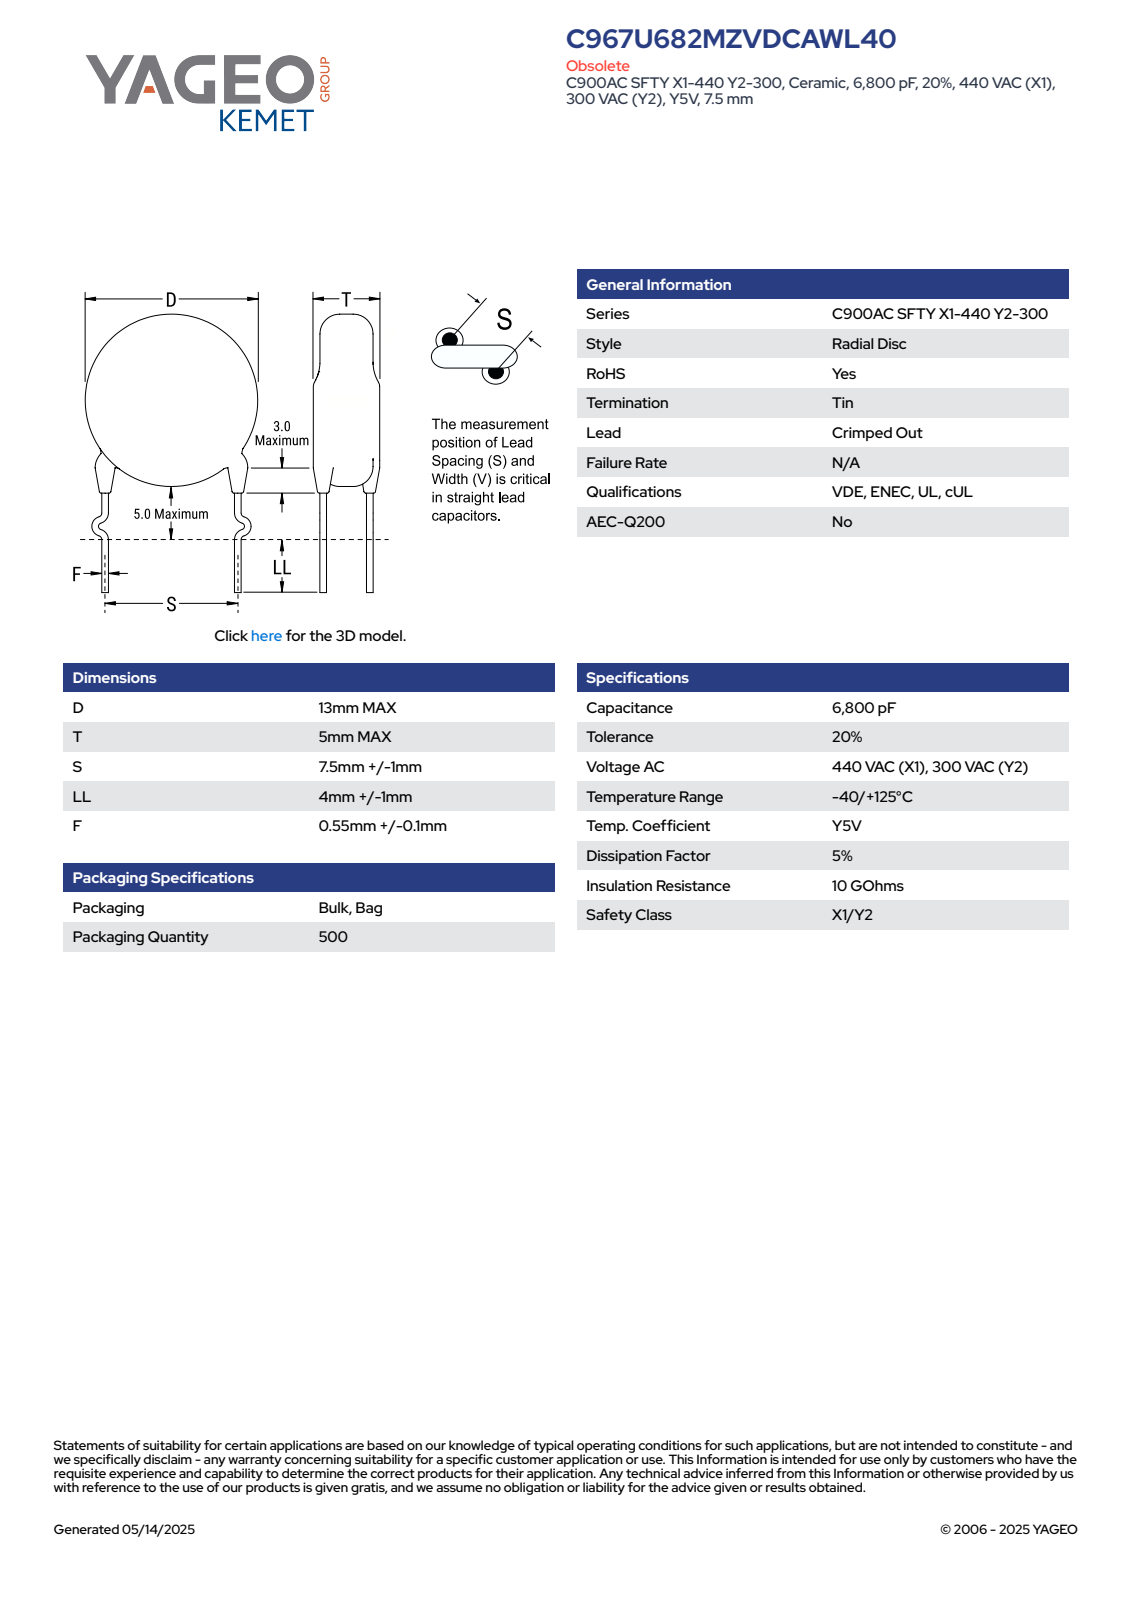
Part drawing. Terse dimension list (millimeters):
name: CCD_KCOC900_D13T5S7.5LL5F0.55
written by: SolidWorks 2014 (AUTOMOTIVE_DESIGN)
unit: mm
bodies: 4 solids, 85 faces (63 planar, 6 cylindrical, 16 other)
size: 23 × 13 × 5
volume: 658 mm³; area: 504 mm²
bosses: 2× ⌀1.2, 1× ⌀13
face distances: 5, 7.19, 5.84, 1.35, 0.37, 0.33, 1.09, 5.52, 2.79, 4.01
